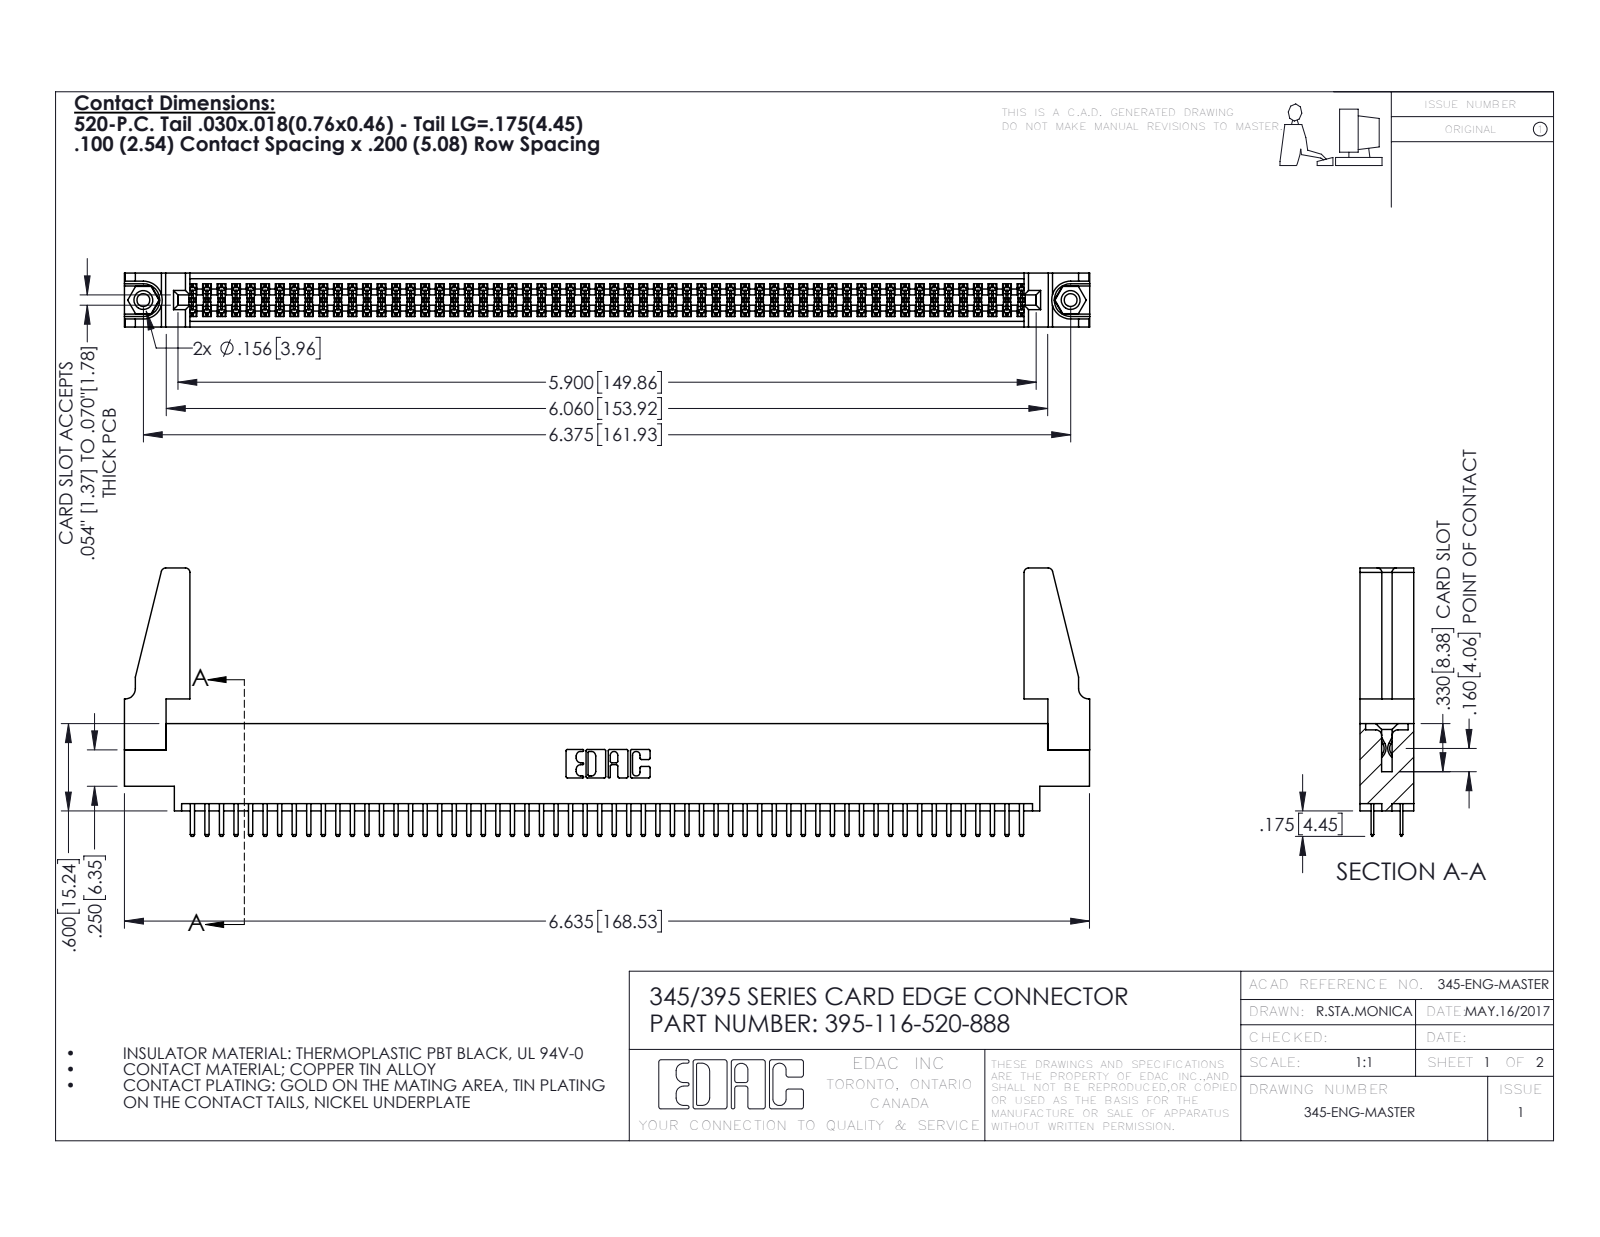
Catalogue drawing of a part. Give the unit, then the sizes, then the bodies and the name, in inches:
Units: inches
Overall size (bounding box): 6.636 × 1.845 × 0.37
Round holes (diameter × count): ⌀0.089 ×2, ⌀0.125 ×2, ⌀0.156 ×2, ⌀0.064 ×1
Round bosses / shafts (diameter × count): ⌀0.155 ×2
Partial cylindrical surfaces — rounded edges, fillets, slot ends (radius × count): R0.006 ×174, R0.01 ×120, R0.01 ×22, R0.03 ×8, R0.007 ×6, R0.031 ×6, R0.026 ×3, R0.014 ×2
Main face-to-face distances: 0.072, 0.298, 0.37, 0.2, 0.098, 0.272, 0.025, 0.225, 0.022, 0.072
Hole centre spacings: 0.27, 6.139, 6.375
Volume: 1.197 in³ · Surface area: 42.85 in²
Bodies: 121 solids, 6518 faces (4216 planar, 2286 cylindrical, 16 other)
Part name (STEP PRODUCT): 345 Part_0.170 Offset - 0.156 Dia-TH; 395-116-520-888; 345-292-001_345-293-120; 345-220-078_345-220-088 (+1 more)
STEP written by: SolidWorks 2016 (CONFIG_CONTROL_DESIGN)
